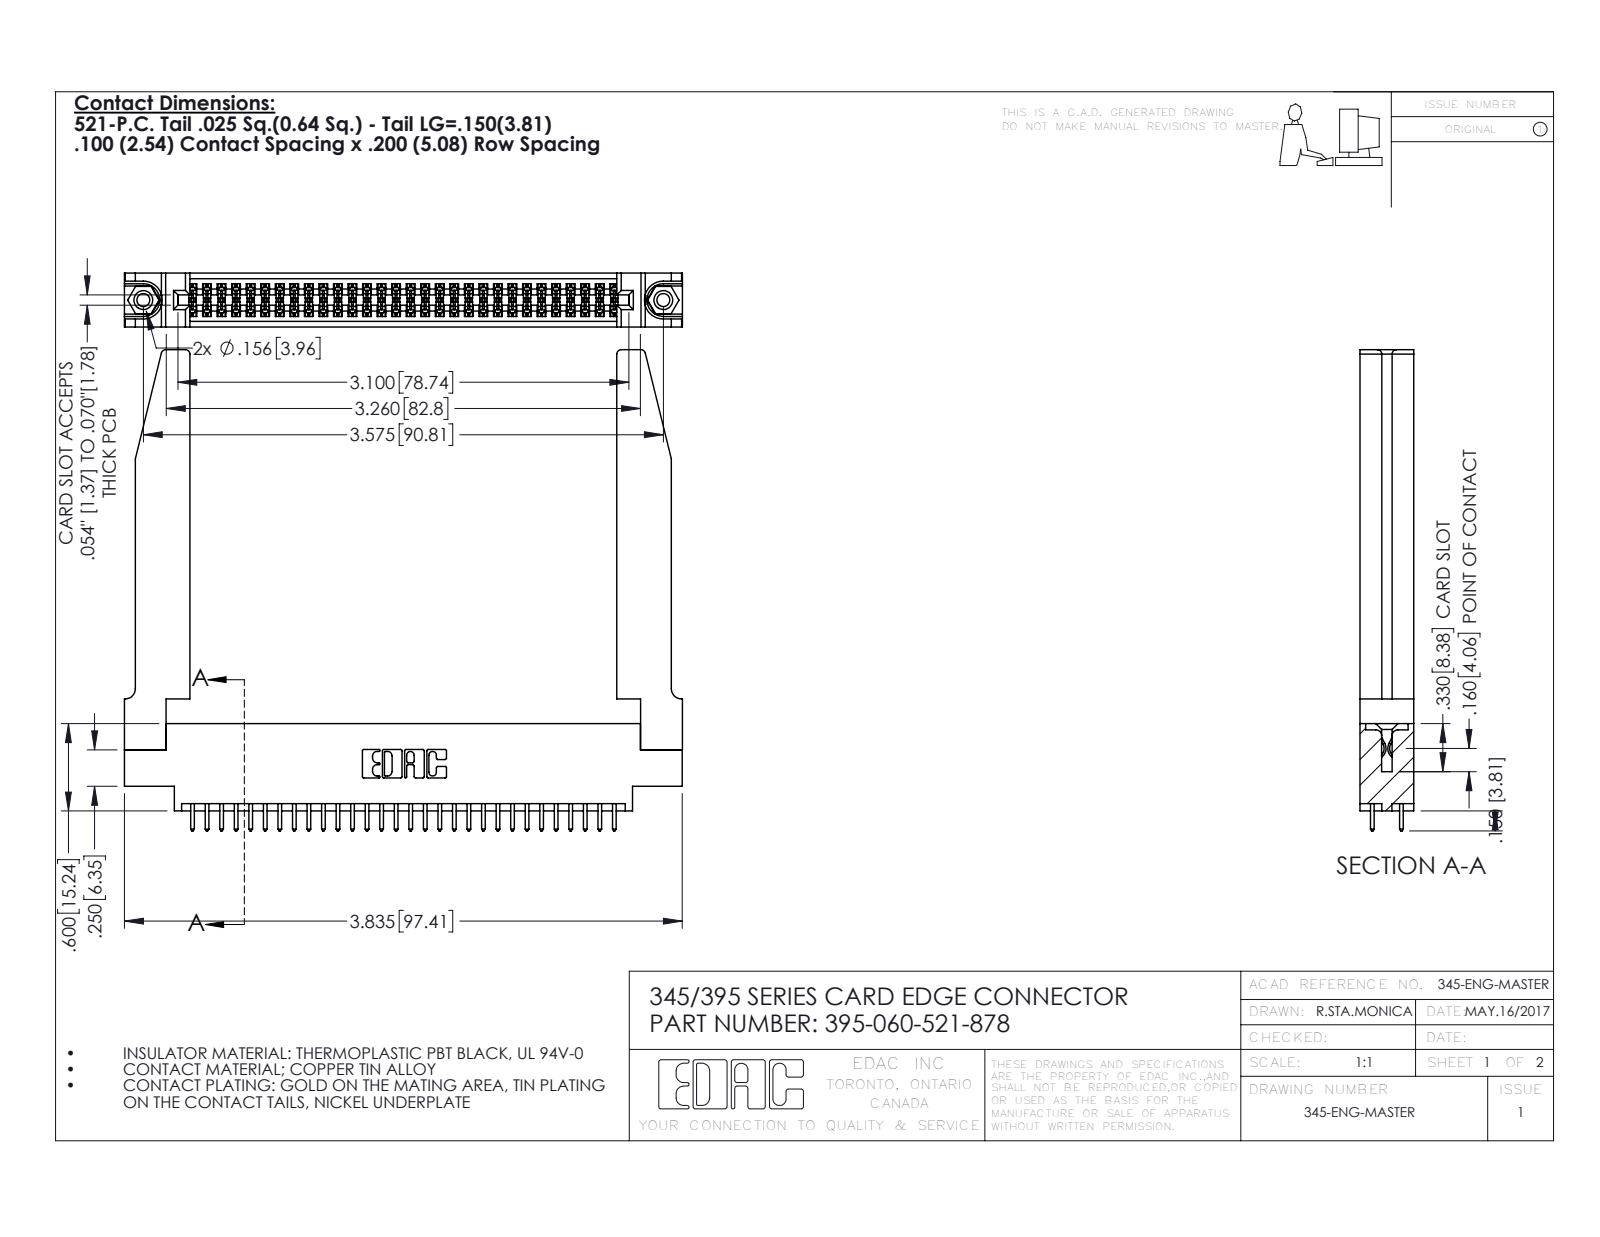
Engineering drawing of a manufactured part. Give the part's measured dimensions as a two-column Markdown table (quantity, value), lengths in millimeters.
| quantity | value |
| --- | --- |
| part name | 345-292-001_345-293-121; 345-250-001_345-250-001-102; 345-220-078_345-220-078; 395-060-521-878 (+1 more) |
| STEP written by | SolidWorks 2016 (CONFIG_CONTROL_DESIGN) |
| units | millimeters |
| bodies | 65 solids, 3364 faces (2206 planar, 1106 cylindrical, 52 other) |
| overall size | 97.4 × 84 × 9.4 |
| volume | 16 990 mm³ |
| surface area | 20 210 mm² |
| round holes (diameter × count) | 2.3 × 2, 3.2 × 2, 4 × 2, 1.6 × 1 |
| round bosses / shafts (diameter × count) | 3.9 × 2 |
| partial cylindrical surfaces (radius × count) | 0.2 × 90, 0.3 × 60, 0.3 × 22, 0.8 × 8, 0.2 × 6, 0.8 × 6, 0.7 × 3, 0.4 × 2 |
| main face-to-face distances | 9.4, 1.8, 7.6, 2.5, 6.9, 0.6, 5.1, 5.7, 4.4, 3.8 |
| hole center spacings | 6.9, 84.8, 90.8 |
